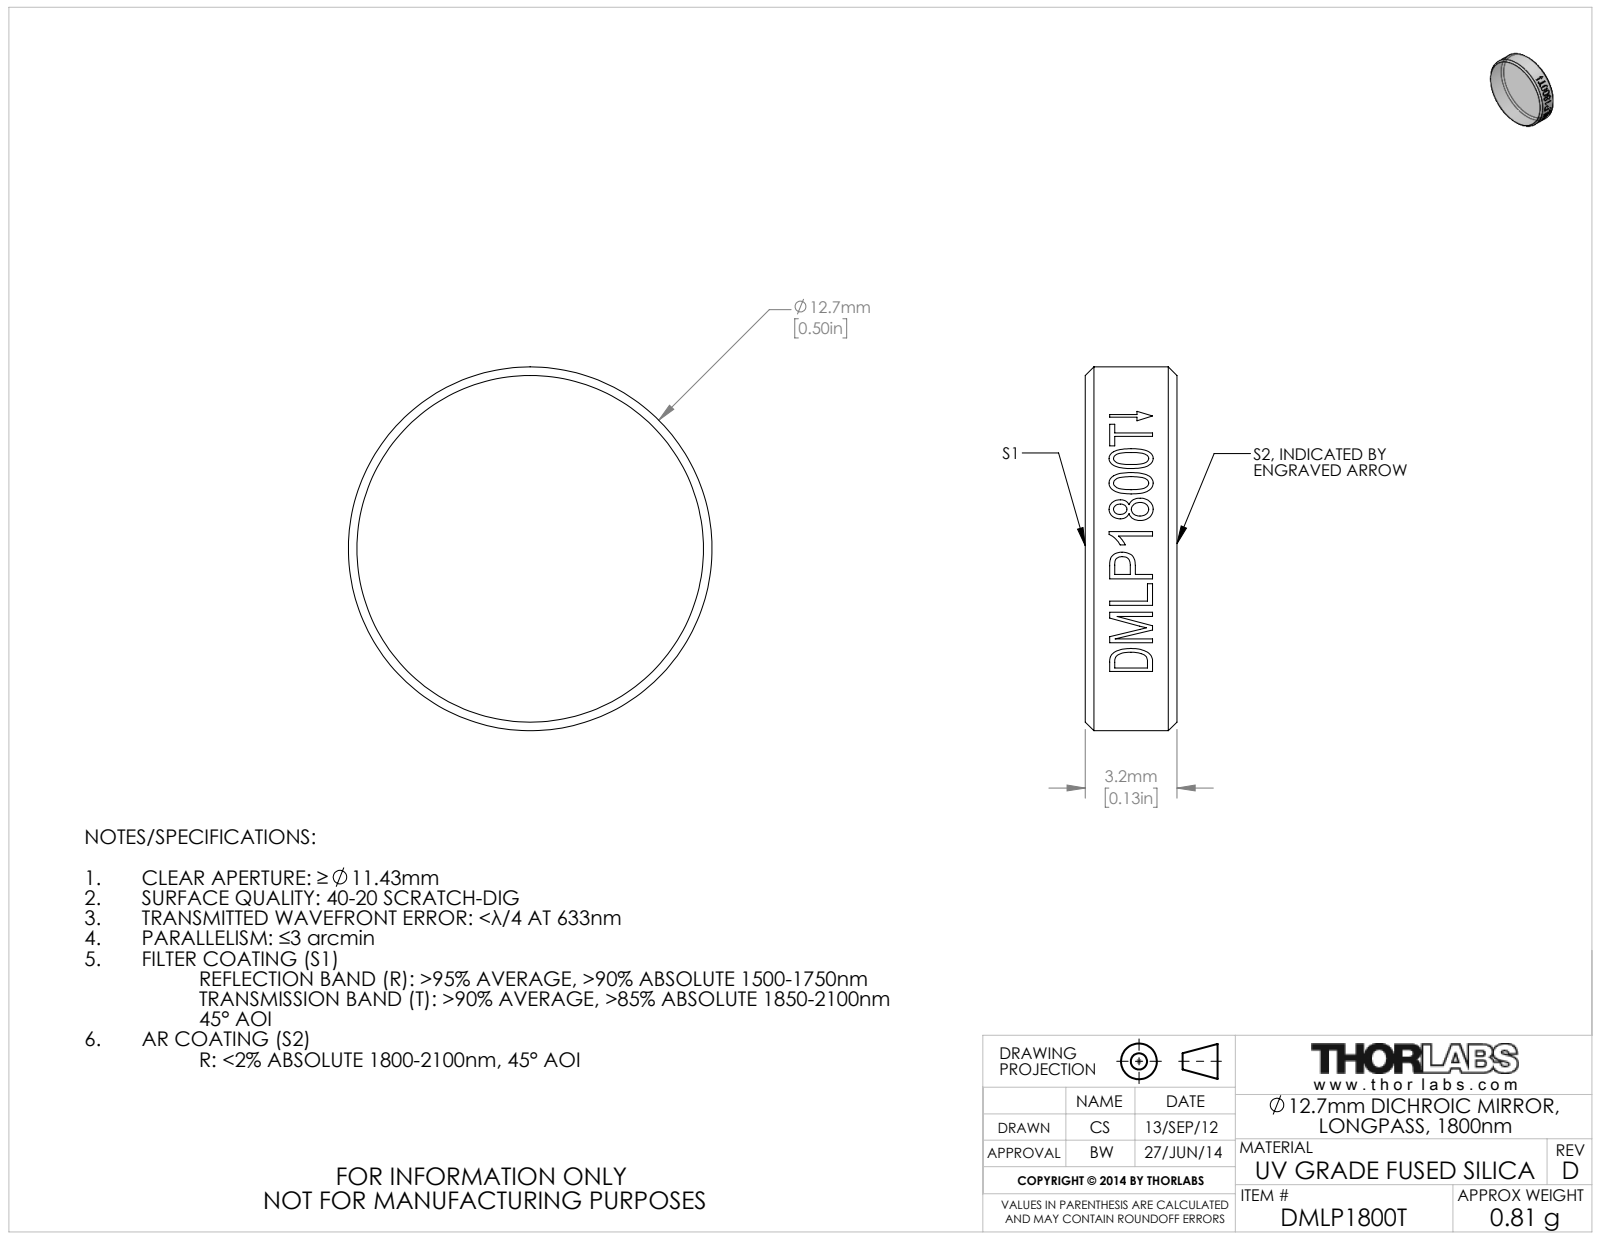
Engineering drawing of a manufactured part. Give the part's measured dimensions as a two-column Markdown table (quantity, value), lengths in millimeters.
| quantity | value |
| --- | --- |
| part name | 24971-E0W |
| STEP written by | SolidWorks 2011 (CONFIG_CONTROL_DESIGN) |
| units | millimeters |
| bodies | 0 solids, 24 faces (2 planar, 18 cylindrical, 4 other) |
| overall size | 12.7 × 12.7 × 3.2 |
| round bosses / shafts (diameter × count) | 12.7 × 1 |
| main face-to-face distances | 3.2 |
